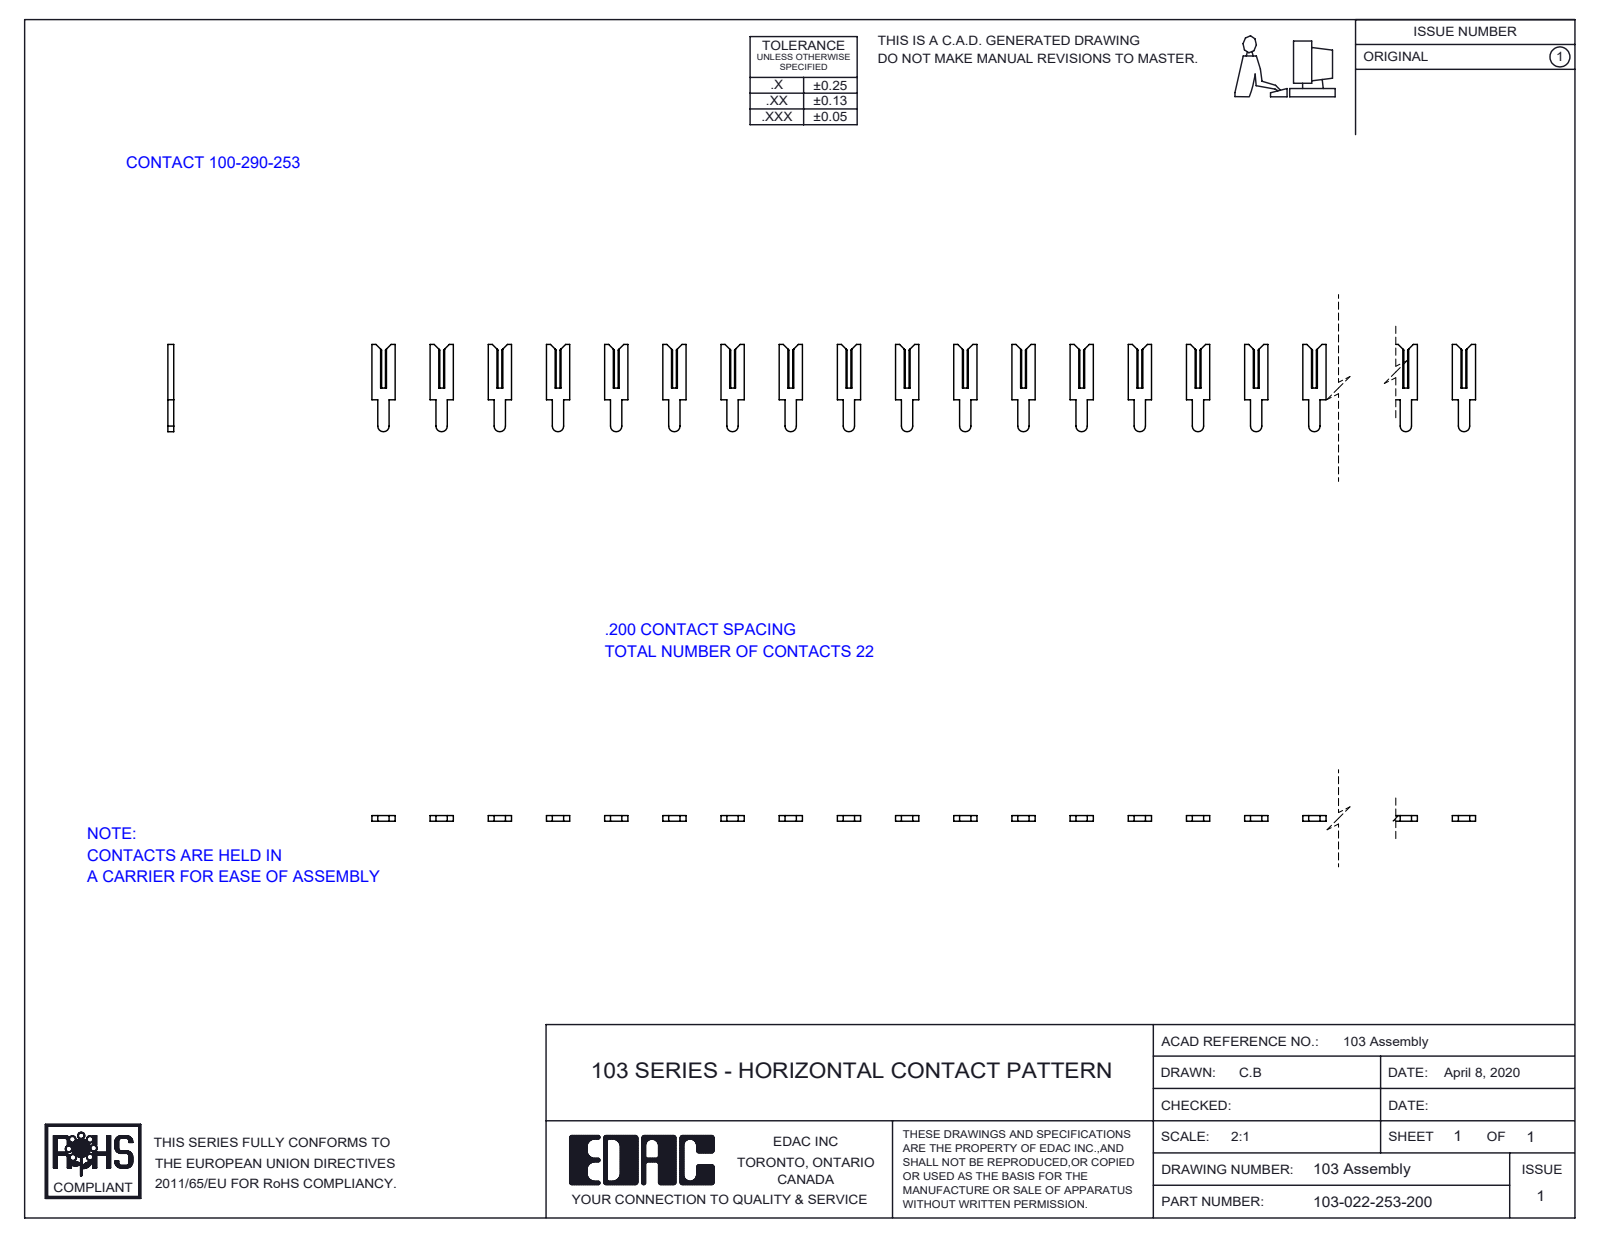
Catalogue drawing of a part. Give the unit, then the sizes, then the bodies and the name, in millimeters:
Units: millimetres
Overall size (bounding box): 108.7 × 7.6 × 0.5
Partial cylindrical surfaces — rounded edges, fillets, slot ends (radius × count): R0.5 ×22
Main face-to-face distances: 0.5, 5.1, 10.2, 3.6, 15.2, 21.5, 7.2, 20.3, 25.1, 18
Volume: 100 mm³ · Surface area: 757 mm²
Bodies: 22 solids, 440 faces (418 planar, 22 cylindrical, 0 other)
Part name (STEP PRODUCT): 100-290-001_100-290-253; 103-022-253-200
STEP written by: SolidWorks 2016 (CONFIG_CONTROL_DESIGN)
